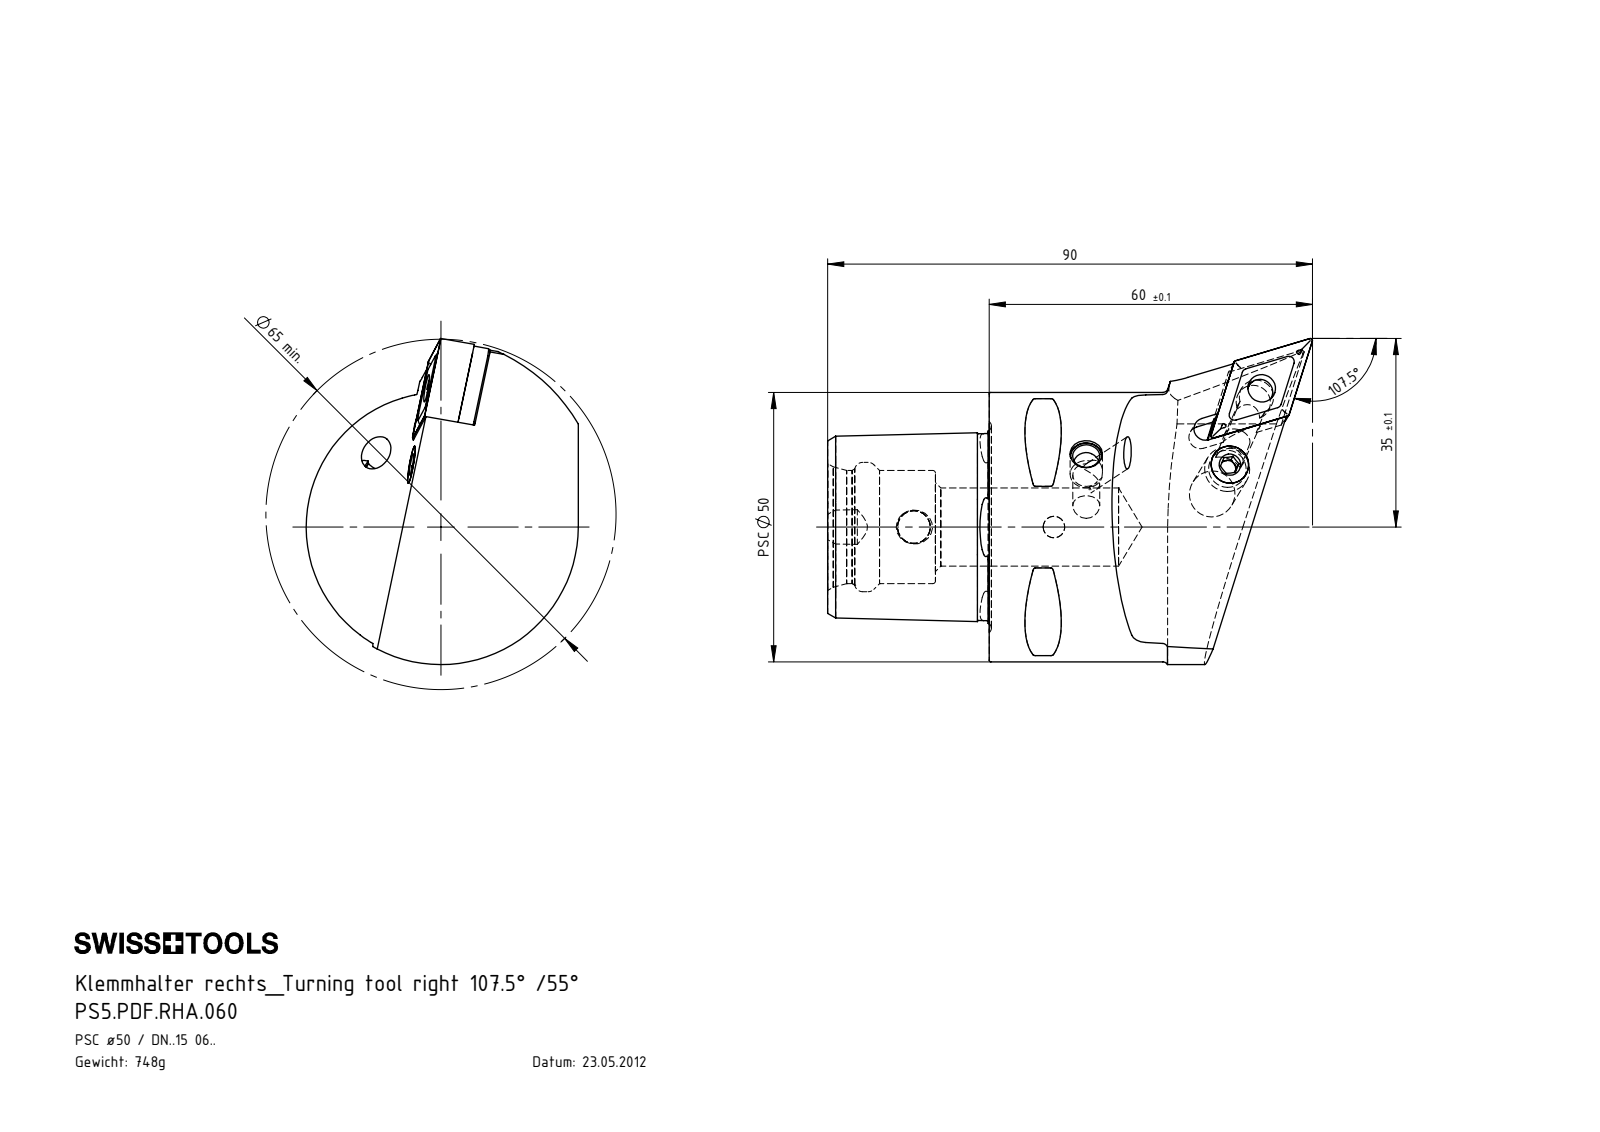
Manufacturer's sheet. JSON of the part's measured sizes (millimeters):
{"part_name": "PS5-PDF.RHA.060; WDF-ER2.101.003_A; WCD-ER4.101.017_A; WCD-ER1.101.000 (+4 more)", "step_written_by": "SolidWorks 2012 (CONFIG_CONTROL_DESIGN)", "units": "millimeters", "bodies": {"solids": 8, "faces": 333, "planar": 90, "cylindrical": 81, "other": 162}, "overall_size": [90, 60.5, 50.5], "volume_mm3": 96086, "surface_area_mm2": 22371, "round_holes": [[5, 3], [4, 1], [5.16, 1], [6, 1], [6.1, 1], [6.4, 1], [7, 1], [8.4, 1], [14.5, 1], [21, 1], [24, 1]], "round_bosses_or_shafts": [[50, 1], [8, 1], [7.9, 1], [6.4, 1], [6, 1], [4.7, 1], [3.55, 1]], "partial_cylinders_radius": [[0.5, 8], [0.4, 4], [1, 4], [2.5, 2], [3.2, 2], [2.1, 1], [2.35, 1], [2.8, 1]], "face_to_face_distances": [30, 6.02, 12.33, 12.3, 19.18, 9.2, 3.17, 9.19, 44.4, 3.18], "hole_center_spacings": [15.61, 26]}
